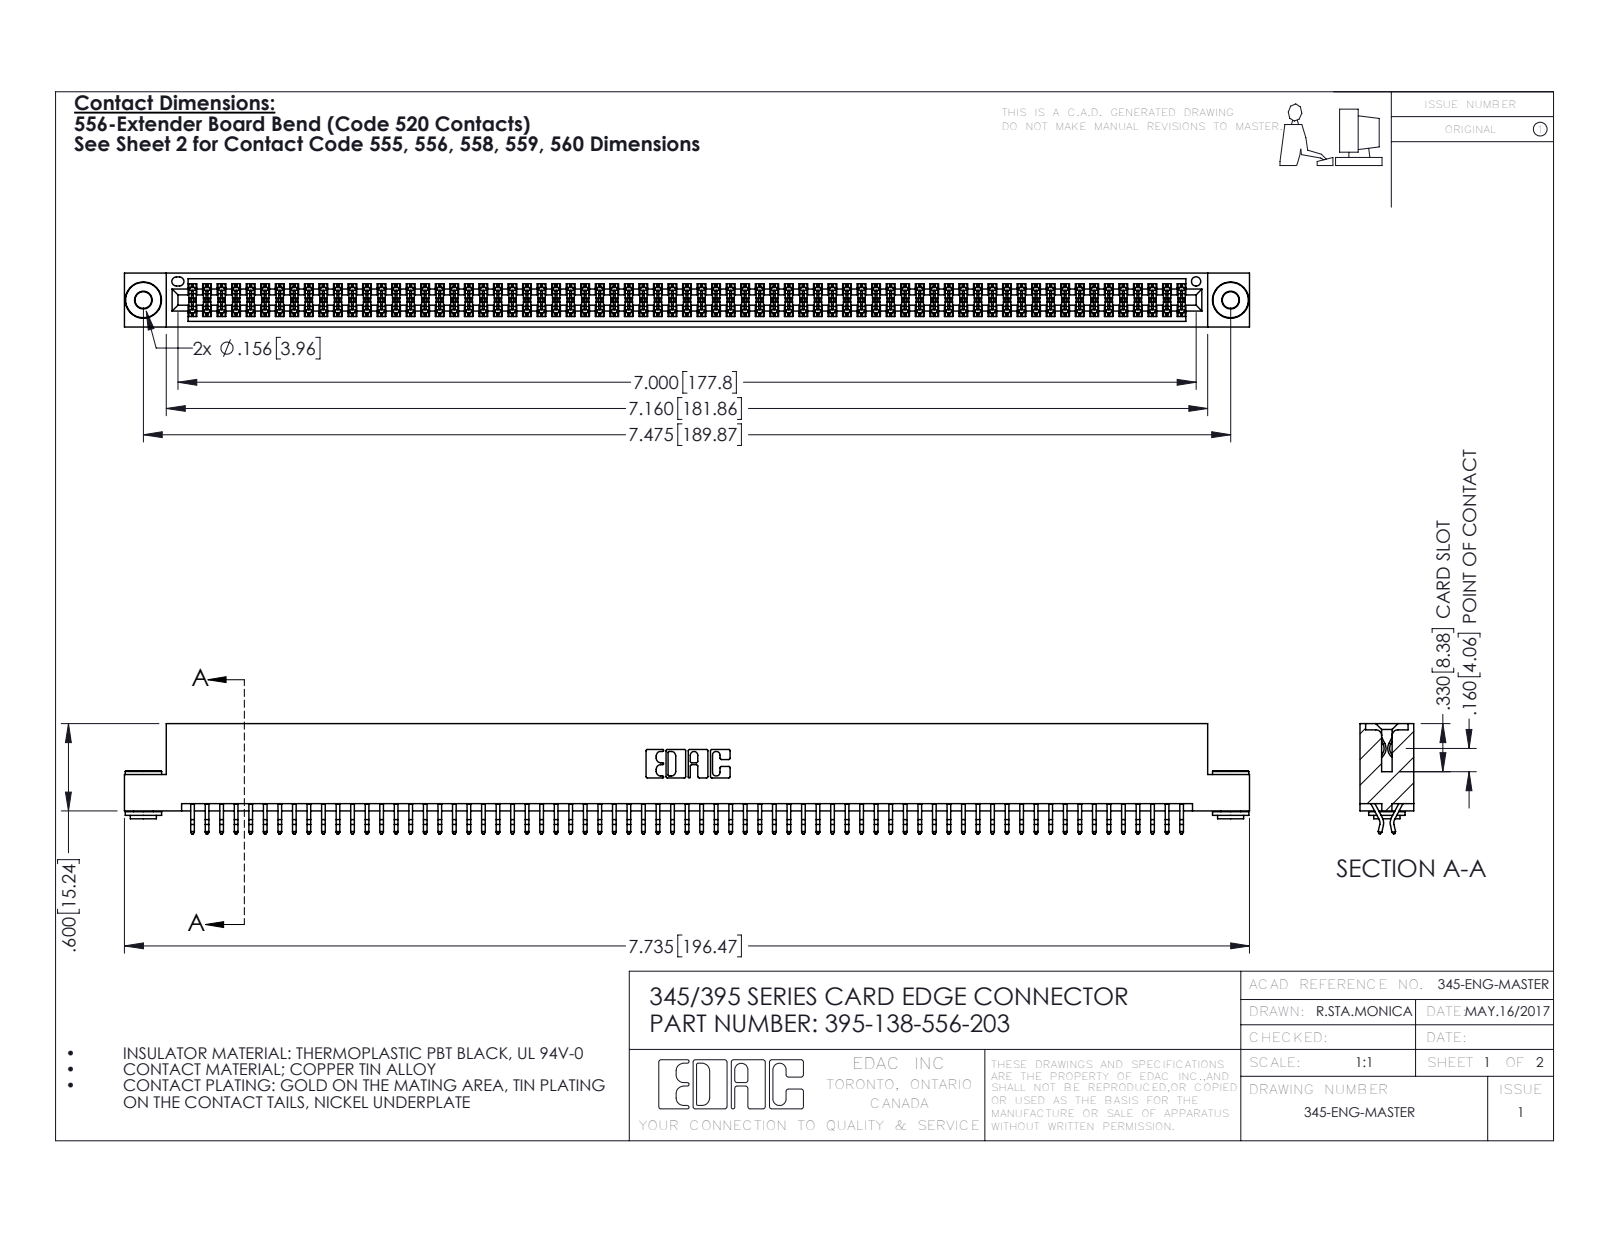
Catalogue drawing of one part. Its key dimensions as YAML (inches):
part_name: "345-292-001_556 Tail; 395-138-556-203; 345 Part_Flush Mounting Lugs - 0.156 Dia-TH; 345-250-002_345-250-002-102"
step_written_by: "SolidWorks 2016 (CONFIG_CONTROL_DESIGN)"
units: inches
bodies: {solids: 141, faces: 7892, planar: 5196, cylindrical: 2688, other: 8}
overall_size: [7.735, 0.757, 0.37]
volume: 1.181
surface_area: 45.27
round_holes:
  - {diameter: 0.116, count: 2}
  - {diameter: 0.156, count: 2}
  - {diameter: 0.064, count: 1}
round_bosses_or_shafts:
  - {diameter: 0.25, count: 2}
  - {diameter: 0.18, count: 2}
  - {diameter: 0.136, count: 2}
partial_cylinders:
  - {radius: 0.006, count: 207}
  - {radius: 0.01, count: 22}
  - {radius: 0.007, count: 6}
  - {radius: 0.031, count: 6}
  - {radius: 0.026, count: 3}
  - {radius: 0.01, count: 2}
  - {radius: 0.014, count: 2}
  - {radius: 0.019, count: 2}
face_to_face_distances: [0.072, 0.298, 0.37, 0.2, 0.025, 0.098, 0.272, 0.225, 0.175, 0.149]
hole_center_spacings: [0.27, 7.239, 7.475]
